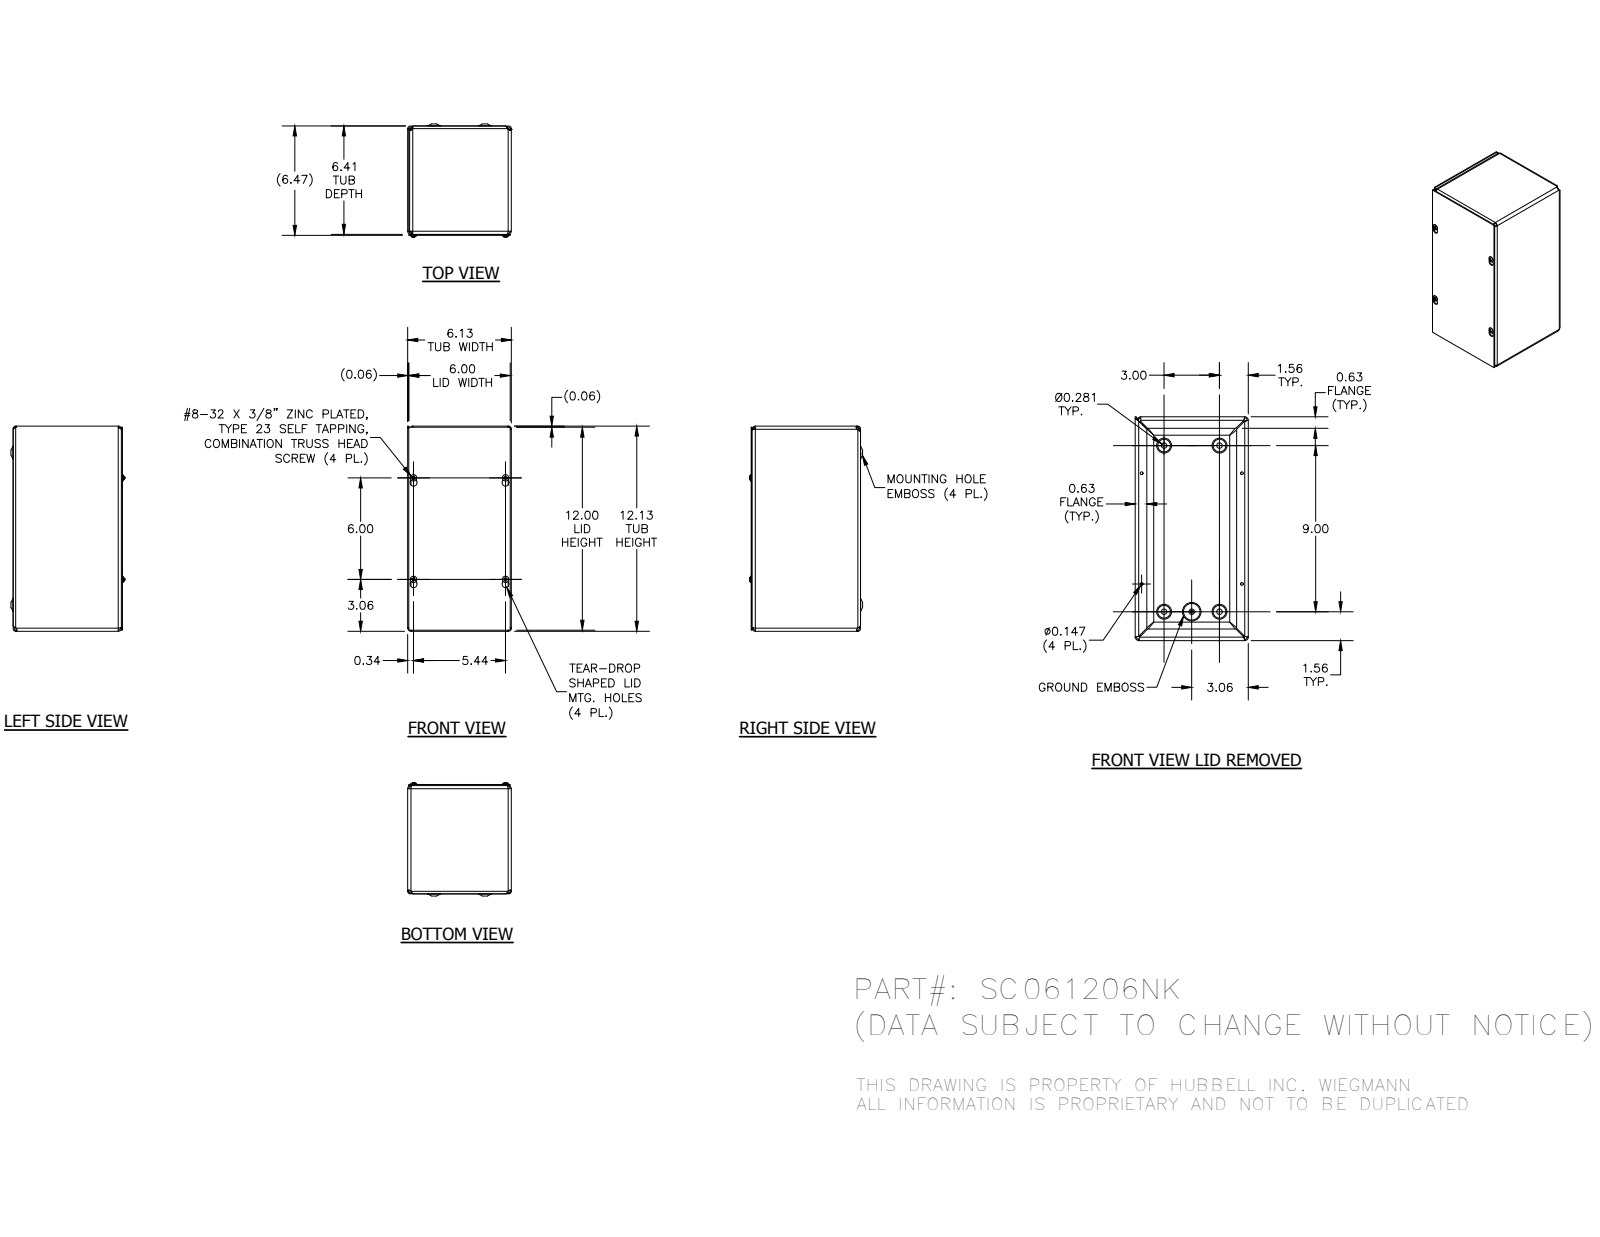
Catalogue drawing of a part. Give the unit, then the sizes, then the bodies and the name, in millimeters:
Units: millimetres
Overall size (bounding box): 307.98 × 170 × 155.57
Round holes (diameter × count): ⌀3.73 ×4, ⌀7.62 ×4, ⌀4.19 ×1
Round bosses / shafts (diameter × count): ⌀9.75 ×4, ⌀4.17 ×4, ⌀5.8 ×1
Partial cylindrical surfaces — rounded edges, fillets, slot ends (radius × count): R3.17 ×12, R4.75 ×8, R1.4 ×4, R1.57 ×4, R2.38 ×4, R2.97 ×4, R3.15 ×4, R3.96 ×4
Main face-to-face distances: 1.57, 1.58, 161.12, 162.69, 154, 152.43, 155.58, 154.01, 1.59, 162.71
Hole centre spacings: 49.09, 193, 218.57, 38.1, 76.2, 113.72, 113.73, 138.11
Volume: 422 922 mm³ · Surface area: 543 981 mm²
Bodies: 7 solids, 357 faces (132 planar, 67 cylindrical, 158 other)
Part name (STEP PRODUCT): SC0612BKP; SC061206NKWRA; SC0612LID; 34056 (+1 more)
STEP written by: Autodesk Inventor 2014 (AUTOMOTIVE_DESIGN)
